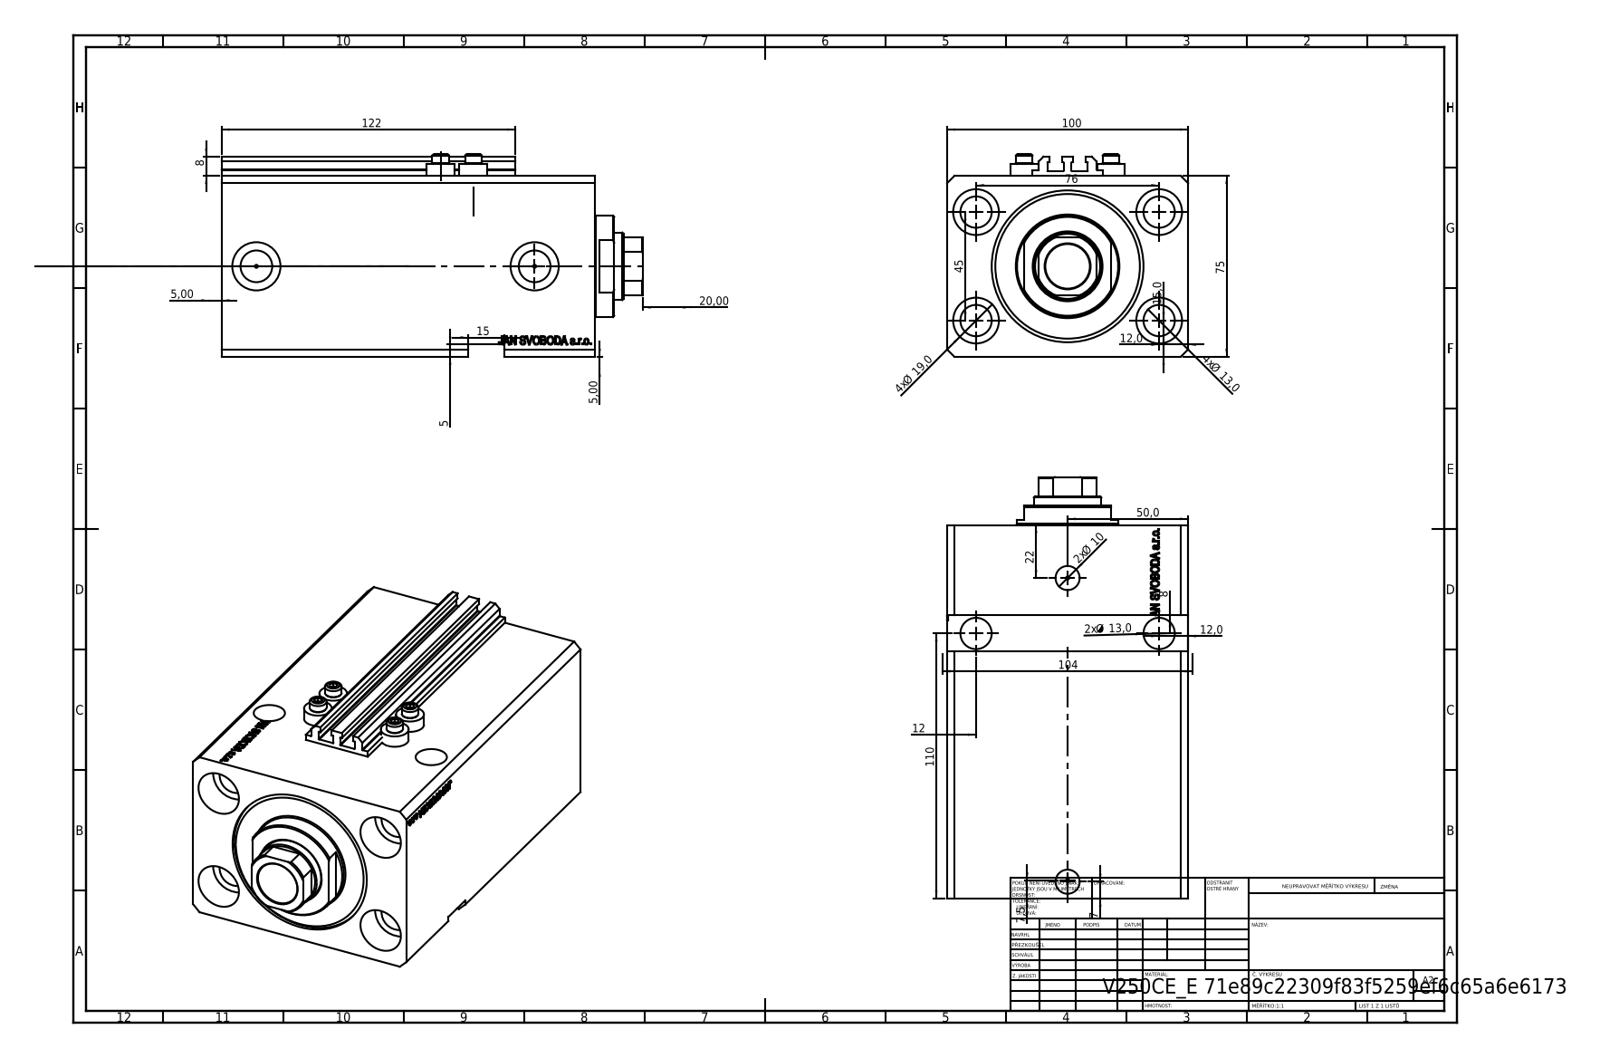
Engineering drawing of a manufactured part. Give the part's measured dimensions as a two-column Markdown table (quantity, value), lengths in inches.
| quantity | value |
| --- | --- |
| part name | V250CE_E_Body; V250CE_VC_E; ALLEN BOLT V250CE; V250CE_C_VCP |
| STEP written by | SolidWorks 2019 (CONFIG_CONTROL_DESIGN) |
| units | inches |
| bodies | 8 solids, 1088 faces (535 planar, 126 cylindrical, 427 other) |
| overall size | 6.886 × 3.937 × 3.307 |
| volume | 58.26 in³ |
| surface area | 270.7 in² |
| round holes (diameter × count) | 0.512 × 6, 0.049 × 4, 0.157 × 4, 0.748 × 4, 0.394 × 2, 0.518 × 2, 0.787 × 2, 0.728 × 1, 1.102 × 1, 1.969 × 1, 2.48 × 1 |
| round bosses / shafts (diameter × count) | 0.457 × 4, 0.276 × 4, 1.654 × 1 |
| partial cylindrical surfaces (radius × count) | 0.008 × 10, 0.531 × 1 |
| main face-to-face distances | 2.953, 3.937, 6.102, 0.469, 5.634, 5.055, 4.587, 1.047, 1.906, 0.315 |
| hole center spacings | 1.739, 2.992, 0.535, 0.816, 1.086, 1.324, 1.417, 1.515 |
